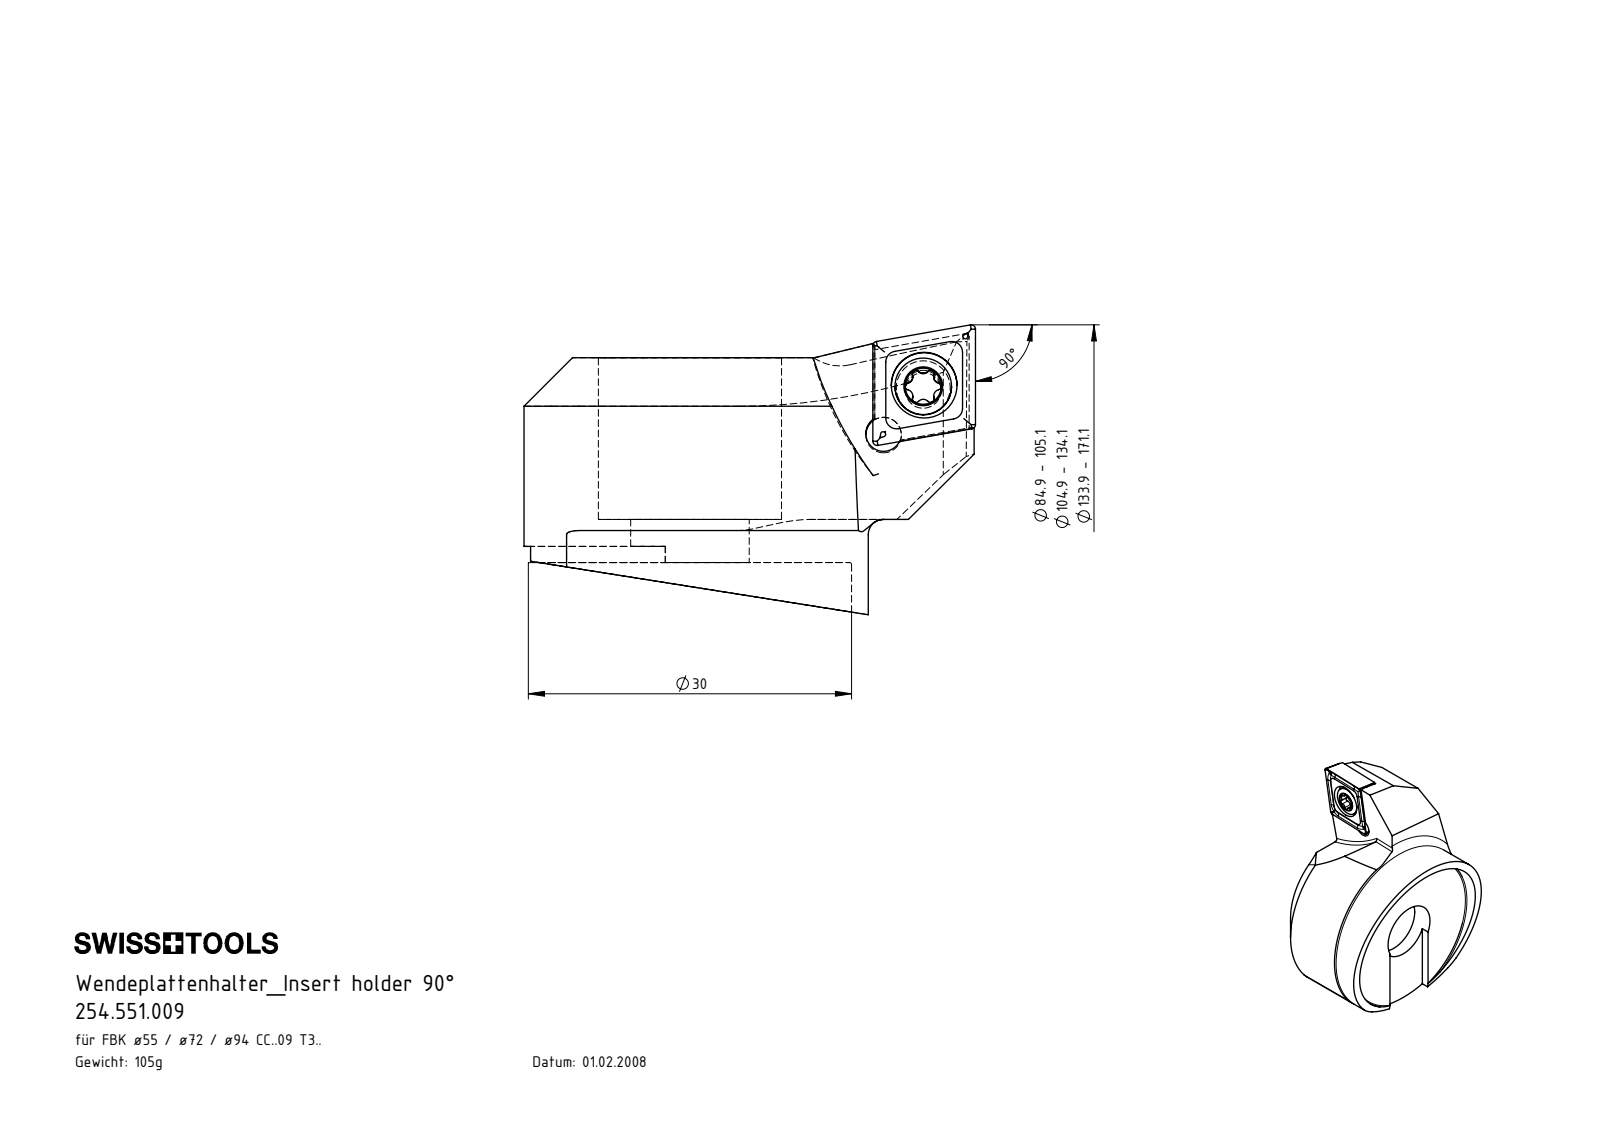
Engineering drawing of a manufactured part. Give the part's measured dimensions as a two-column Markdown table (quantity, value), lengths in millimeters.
| quantity | value |
| --- | --- |
| part name | F55-WCB.001.022_D_fertigbearbeitet; WCB-ER2.001.009_A; F55.WCB.001.022; CCMT09T304 |
| STEP written by | SolidWorks 2017 (AUTOMOTIVE_DESIGN) |
| units | millimeters |
| bodies | 3 solids, 120 faces (41 planar, 31 cylindrical, 48 other) |
| overall size | 41.9 × 33.2 × 26.89 |
| volume | 13 329 mm³ |
| surface area | 5 651 mm² |
| round holes (diameter × count) | 3.3 × 2, 4.4 × 1, 6.1 × 1, 11 × 1, 17 × 1, 30 × 1 |
| round bosses / shafts (diameter × count) | 5.25 × 1, 4 × 1 |
| partial cylindrical surfaces (radius × count) | 0.34 × 6, 0.59 × 6, 0.5 × 2, 10 × 2, 5 × 1, 16.55 × 1, 16.6 × 1, 20.9 × 1 |
| main face-to-face distances | 19, 15, 4, 17.5, 2.5, 1.5, 3.77, 3.97, 10, 9 |
| hole center spacings | 5.73, 5.86 |
